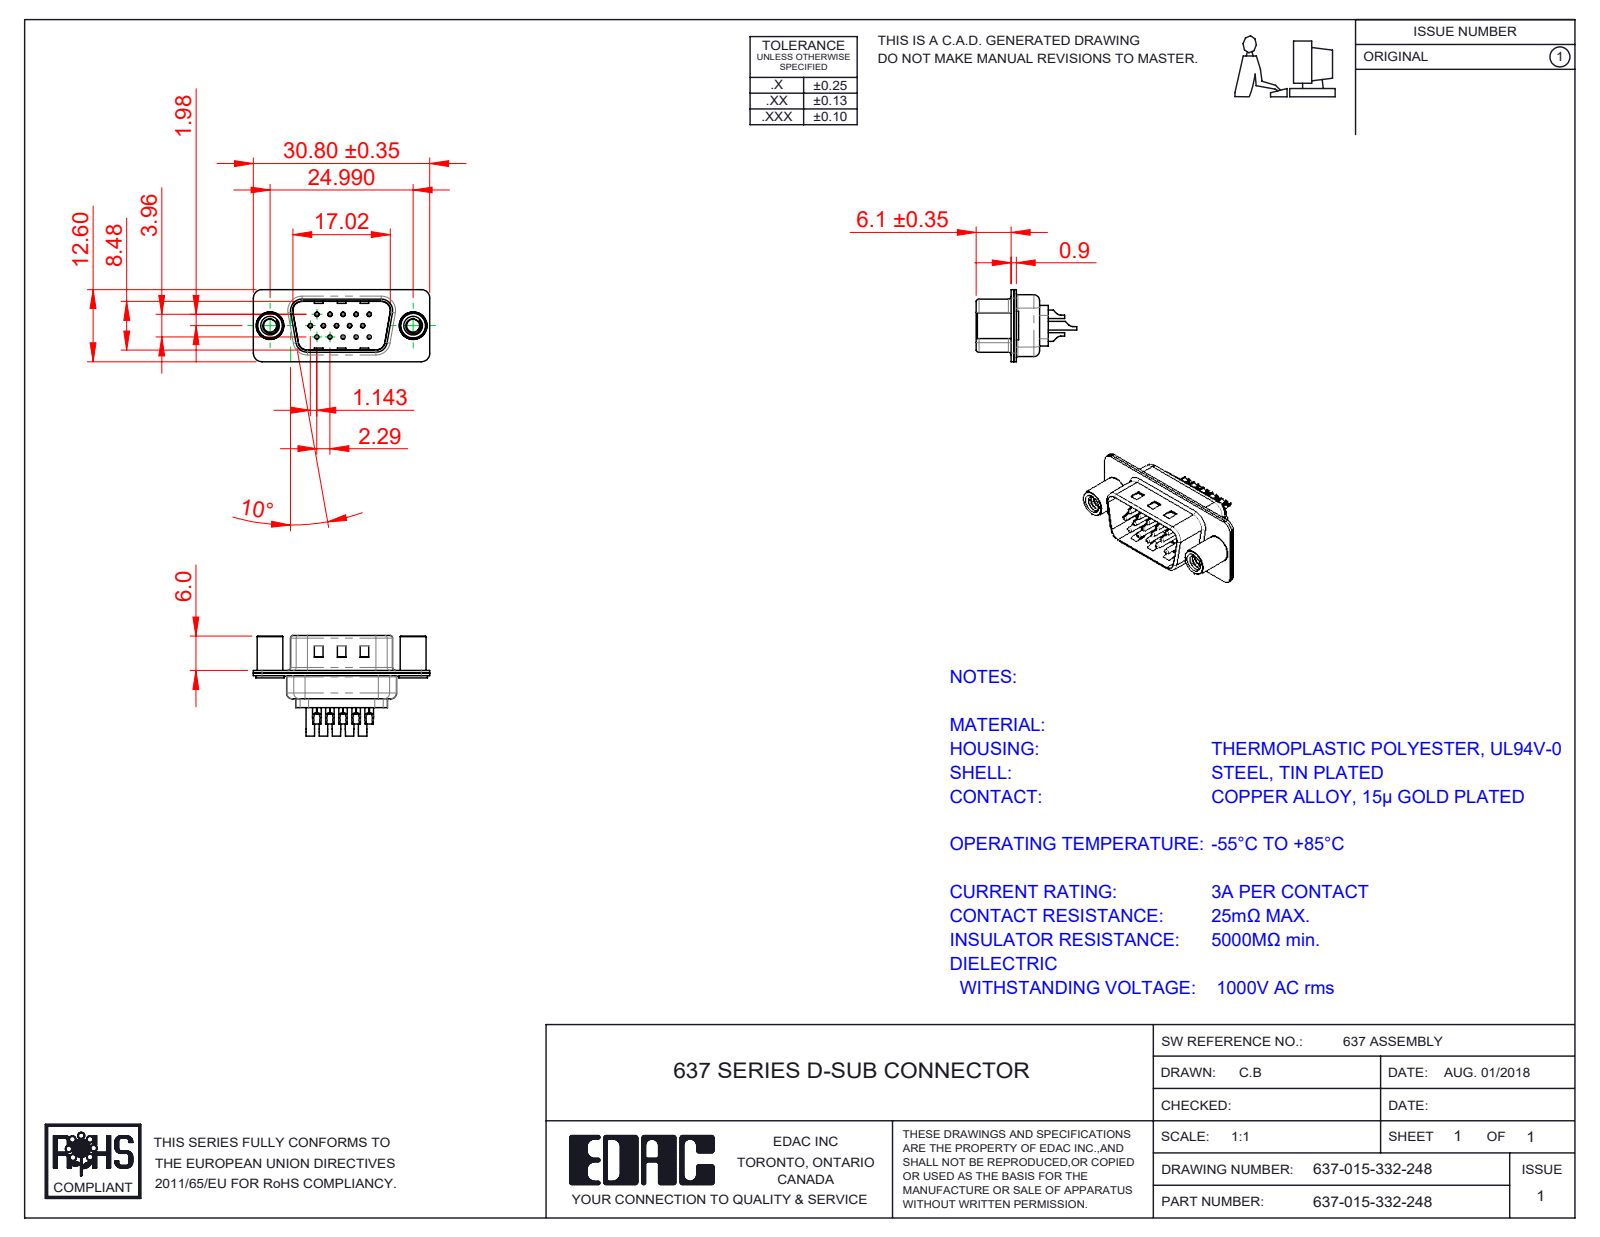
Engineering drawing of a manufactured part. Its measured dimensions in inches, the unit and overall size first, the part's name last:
Units: inches
Overall size (bounding box): 1.213 × 0.691 × 0.496
Round holes (diameter × count): ⌀0.014 ×15, ⌀0.043 ×15, ⌀0.063 ×15, ⌀0.089 ×2, ⌀0.157 ×2, ⌀0.189 ×2
Round bosses / shafts (diameter × count): ⌀0.079 ×15, ⌀0.059 ×15, ⌀0.03 ×15, ⌀0.197 ×2, ⌀0.193 ×2, ⌀0.177 ×2
Partial cylindrical surfaces — rounded edges, fillets, slot ends (radius × count): R0.059 ×16, R0.079 ×12, R0.02 ×8, R0.039 ×7, R0.01 ×4, R0.022 ×4, R0.028 ×4, R0.037 ×4
Main face-to-face distances: 0.018, 0.035, 0.016, 0.028, 0.35, 0.334, 0.041, 0.012, 0.179, 0.046
Hole centre spacings: 0.156, 0.09, 0.18, 0.09, 0.238, 0.27, 0.312, 0.238
Volume: 0.085 in³ · Surface area: 7.707 in²
Bodies: 20 solids, 1298 faces (319 planar, 592 cylindrical, 387 other)
Part name (STEP PRODUCT): 637 Shell Front_15 Contacts; 637 Housing_15 Contacts; 637 Contact Row 1_32; 637 Contact Row 3_32 (+4 more)
STEP written by: SolidWorks 2020 (CONFIG_CONTROL_DESIGN)
